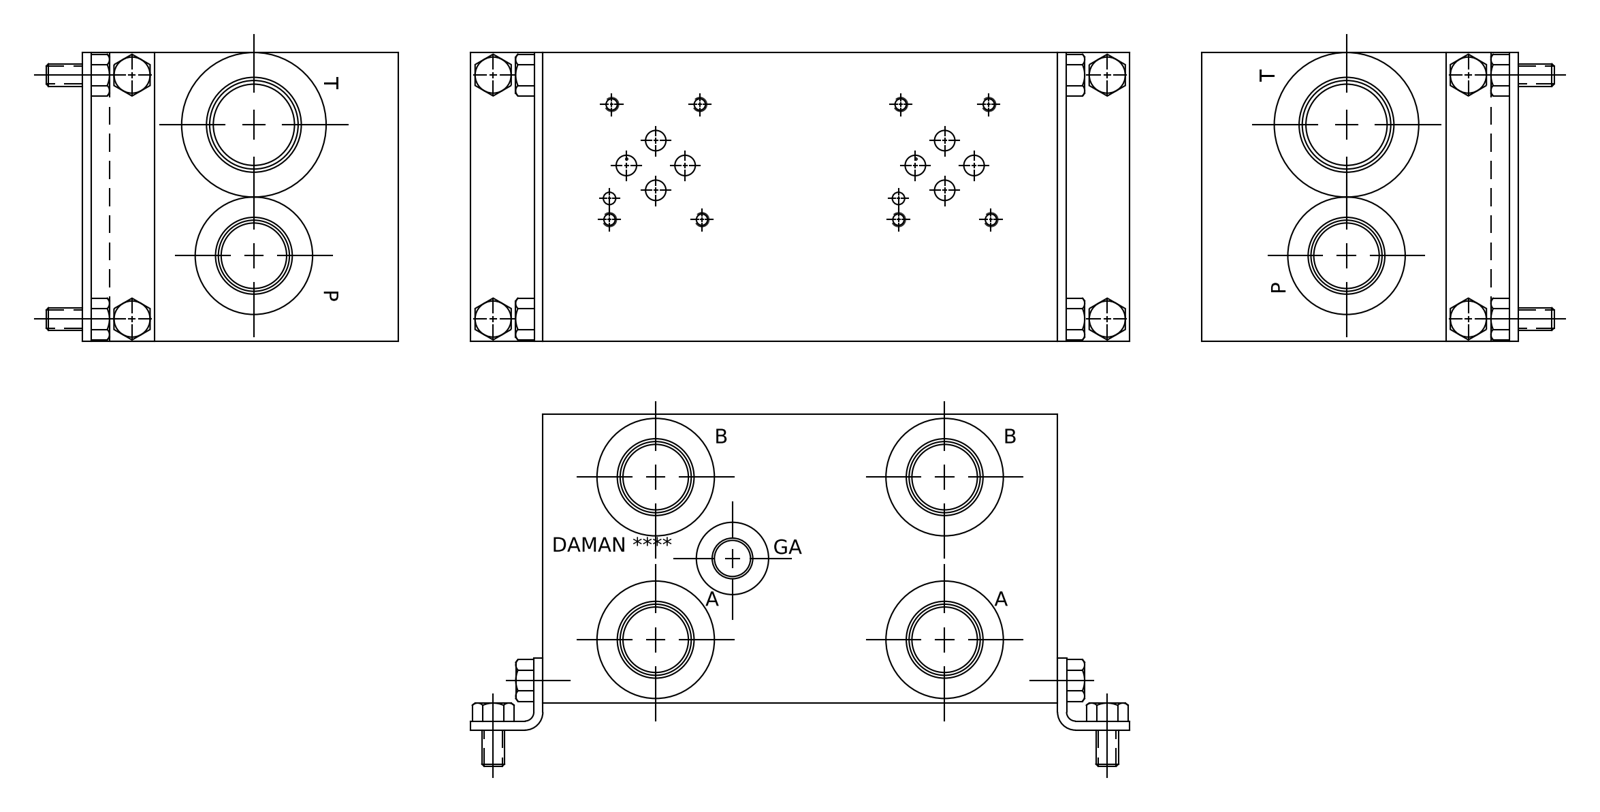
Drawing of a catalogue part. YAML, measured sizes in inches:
part_name: "Part_AD03HP024S_3D"
step_written_by: "Autodesk Inventor 2020 (AUTOMOTIVE_DESIGN)"
units: inches
bodies: {solids: 1, faces: 662, planar: 373, cylindrical: 79, other: 210}
overall_size: [7.125, 4, 4]
volume: 103.3
surface_area: 187.7
round_holes:
  - {diameter: 0.149, count: 8}
  - {diameter: 0.19, count: 8}
  - {diameter: 0.25, count: 6}
  - {diameter: 0.906, count: 5}
  - {diameter: 0.981, count: 5}
  - {diameter: 1.063, count: 5}
  - {diameter: 1.08, count: 5}
  - {diameter: 1.655, count: 5}
  - {diameter: 0.156, count: 2}
  - {diameter: 0.257, count: 2}
  - {diameter: 0.281, count: 2}
  - {diameter: 0.312, count: 2}
face_to_face_distances: [4, 7.125, 0.031, 3.969, 7.094, 0.031, 7.063, 7.094, 0.75, 0.781]
hole_center_spacings: [4, 0.532, 0.533, 0.868, 1.321, 1.594, 2.026, 0.295]
